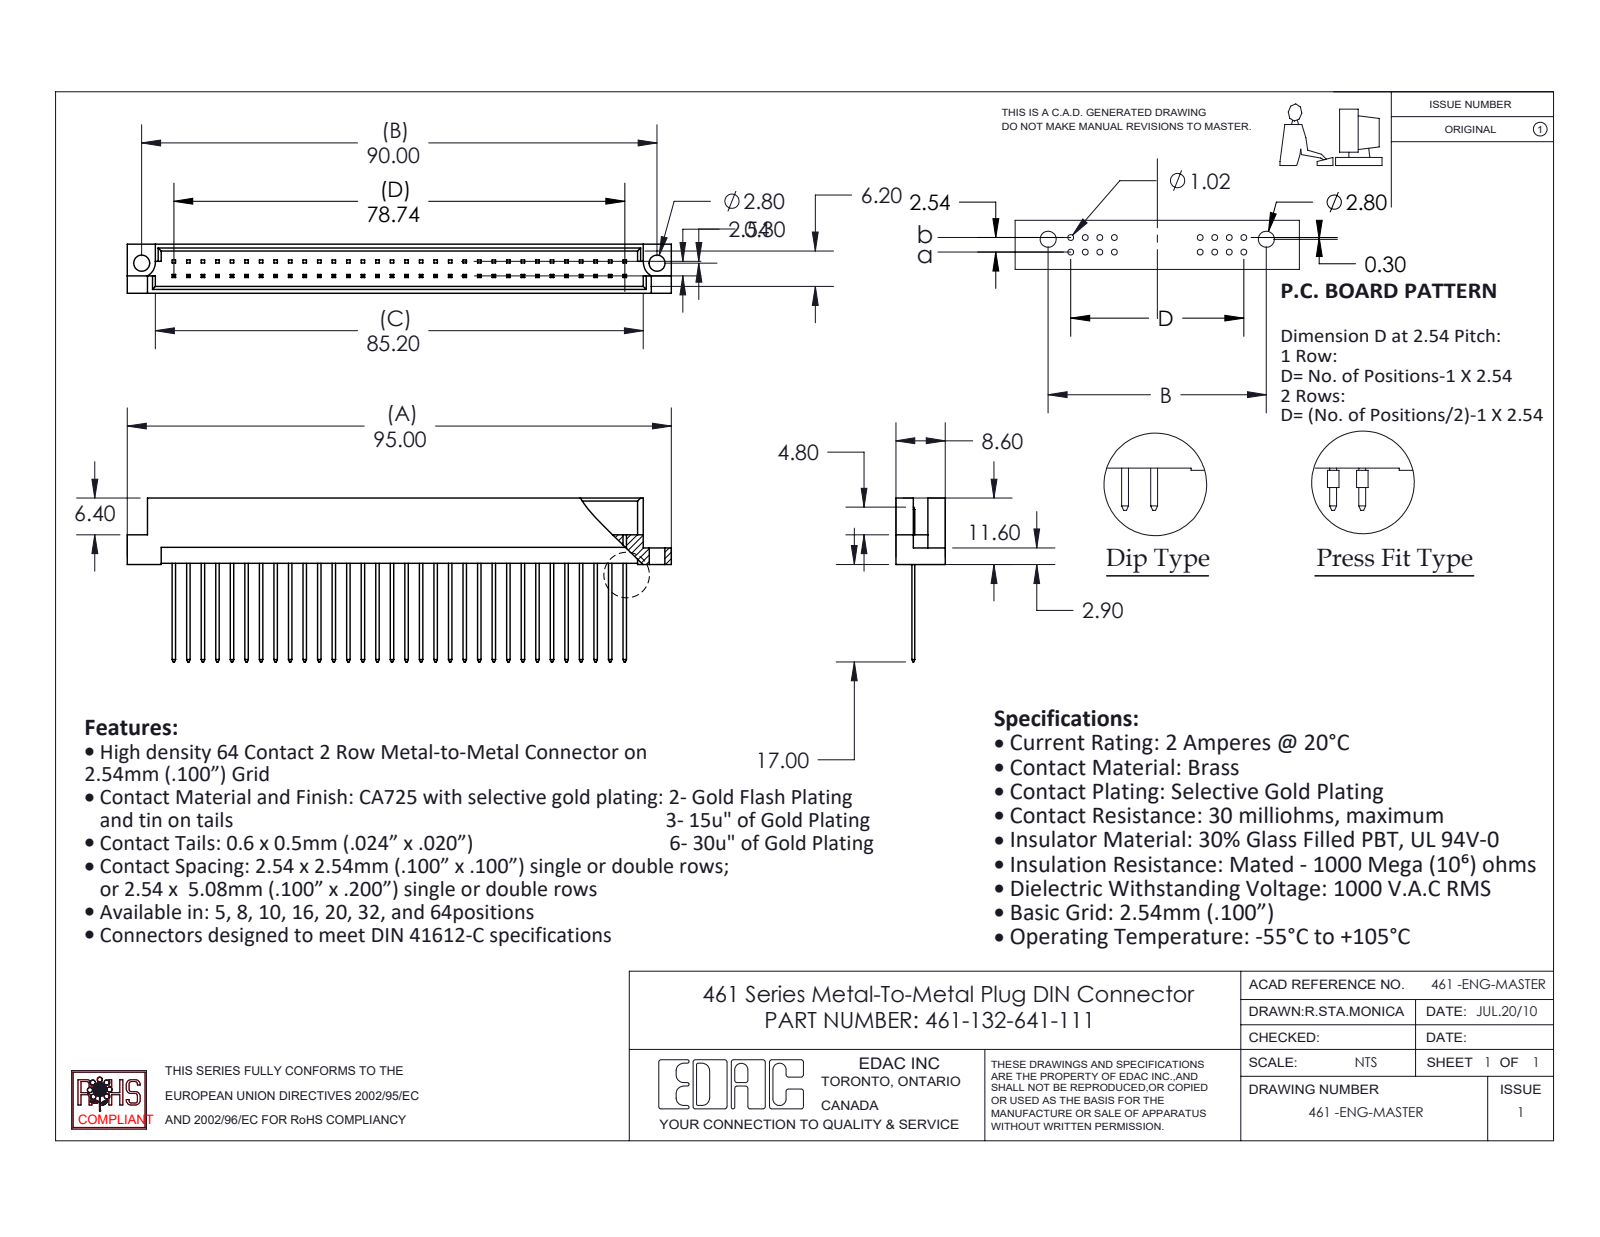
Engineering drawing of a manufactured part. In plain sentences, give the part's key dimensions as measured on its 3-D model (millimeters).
The part is named "461 Part_64; 461-132-641-111; 461-290_41". Its 3-D file was written by "SolidWorks 2020 (CONFIG_CONTROL_DESIGN)". It is 33 solids with 753 faces: 746 planar, 7 cylindrical and 0 other. Overall it measures 95 by 28.6 by 8.6 millimeters. Its volume is 4 912 cubic millimeters and its surface area 7 560 square millimeters. Round holes: 2 of diameter 2.8. Partial cylindrical surfaces (rounded edges, fillets, slot ends): 2 of radius 2.8. The main face-to-face distances are 1.2, 7.4, 8.6, 6.2, 3.28, 5.32, 2.08, 4.12, 2.78, 5.82. The hole center spacings are 90.
